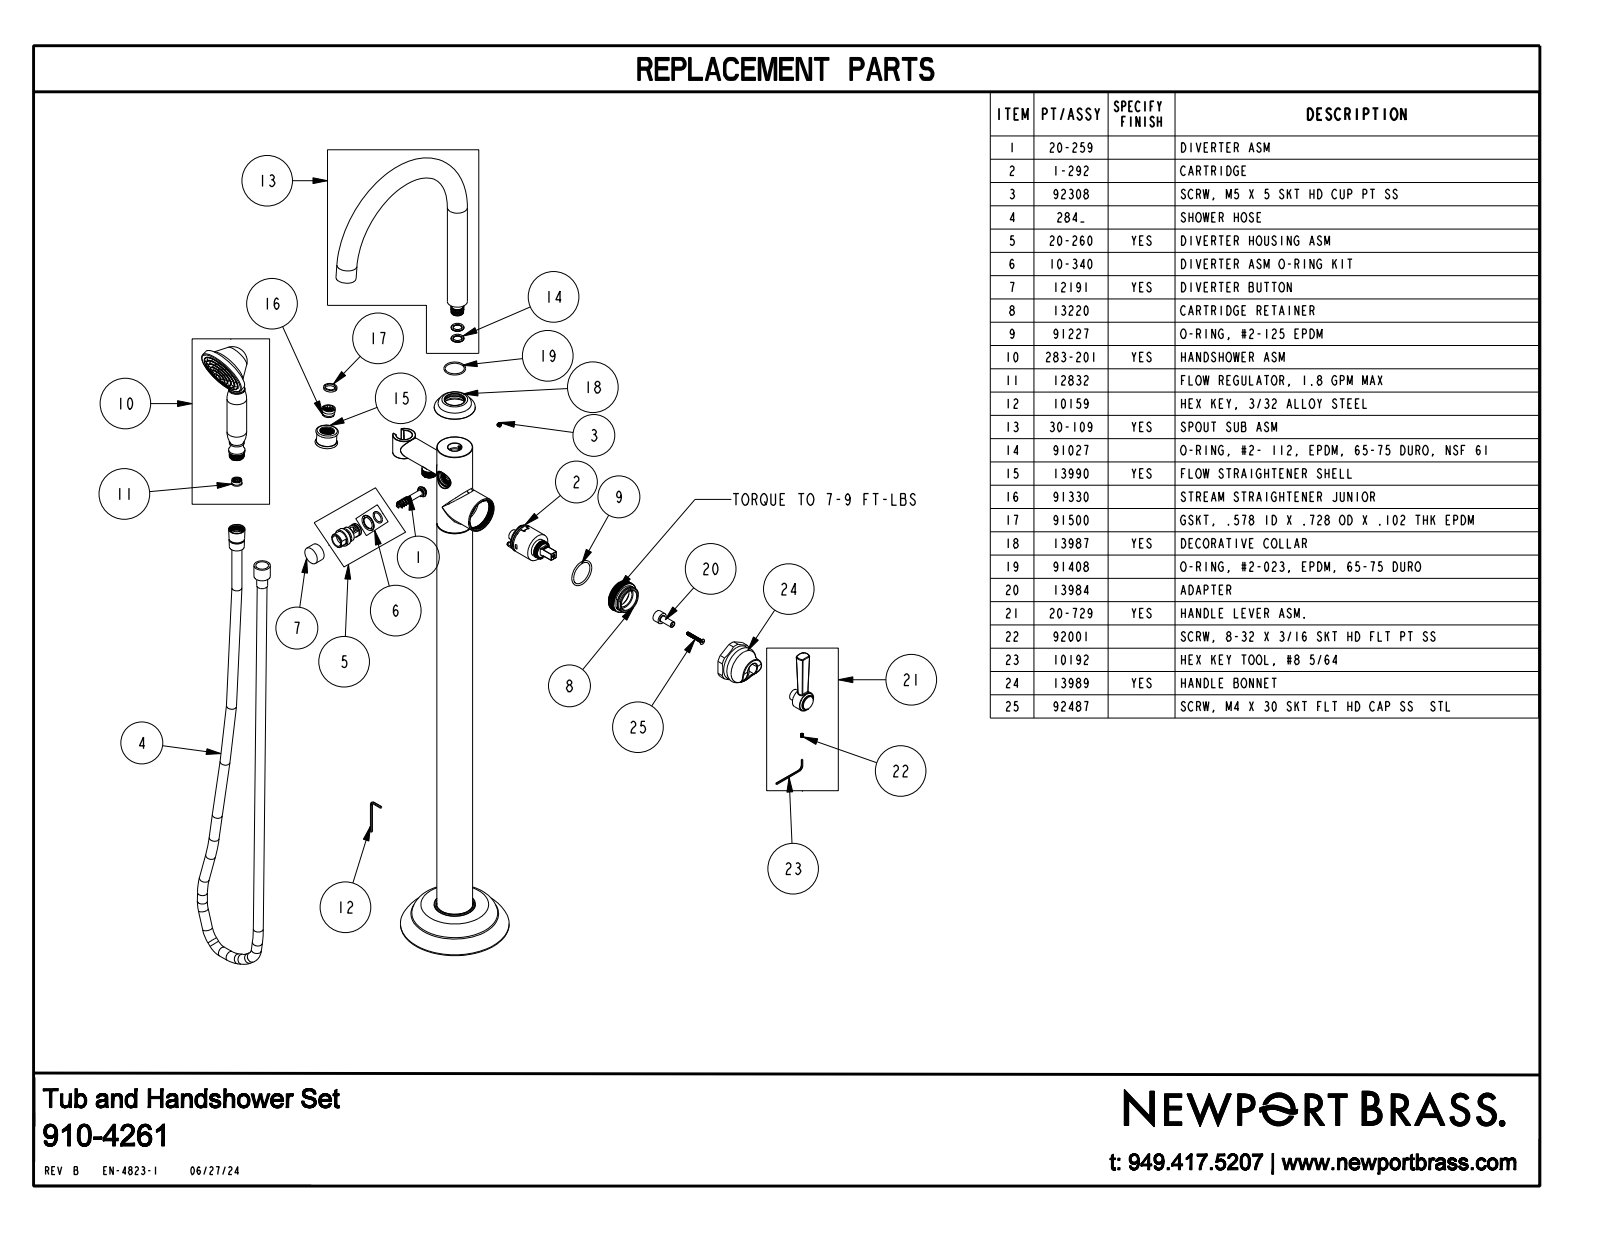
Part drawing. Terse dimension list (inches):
name: 910-4261
written by: CREO PARAMETRIC BY PTC INC, 2023134 (CONFIG_CONTROL_DESIGN)
unit: in
bodies: 1 solid, 594 faces (94 planar, 245 cylindrical, 255 other)
size: 43.307 × 12.333 × 11.284
volume: 179.5 in³; area: 516 in²
holes: 59× ⌀0.031, 1× ⌀0.118, 1× ⌀0.516, 1× ⌀0.606, 1× ⌀0.656
bosses: 14× ⌀0.55, 2× ⌀1.969, 2× ⌀1.102, 2× ⌀0.9, 1× ⌀5.979, 1× ⌀2.875, 1× ⌀2.43, 1× ⌀2.04
rounds: 6× R0.02, 2× R0.355, 1× R0.3, 1× R0.63, 1× R0.681, 1× R0.947, 1× R1.12
face distances: 1.335, 0.31, 32.126, 30.791, 2.094, 0.55, 0.692, 1.402, 1.724, 32.676
